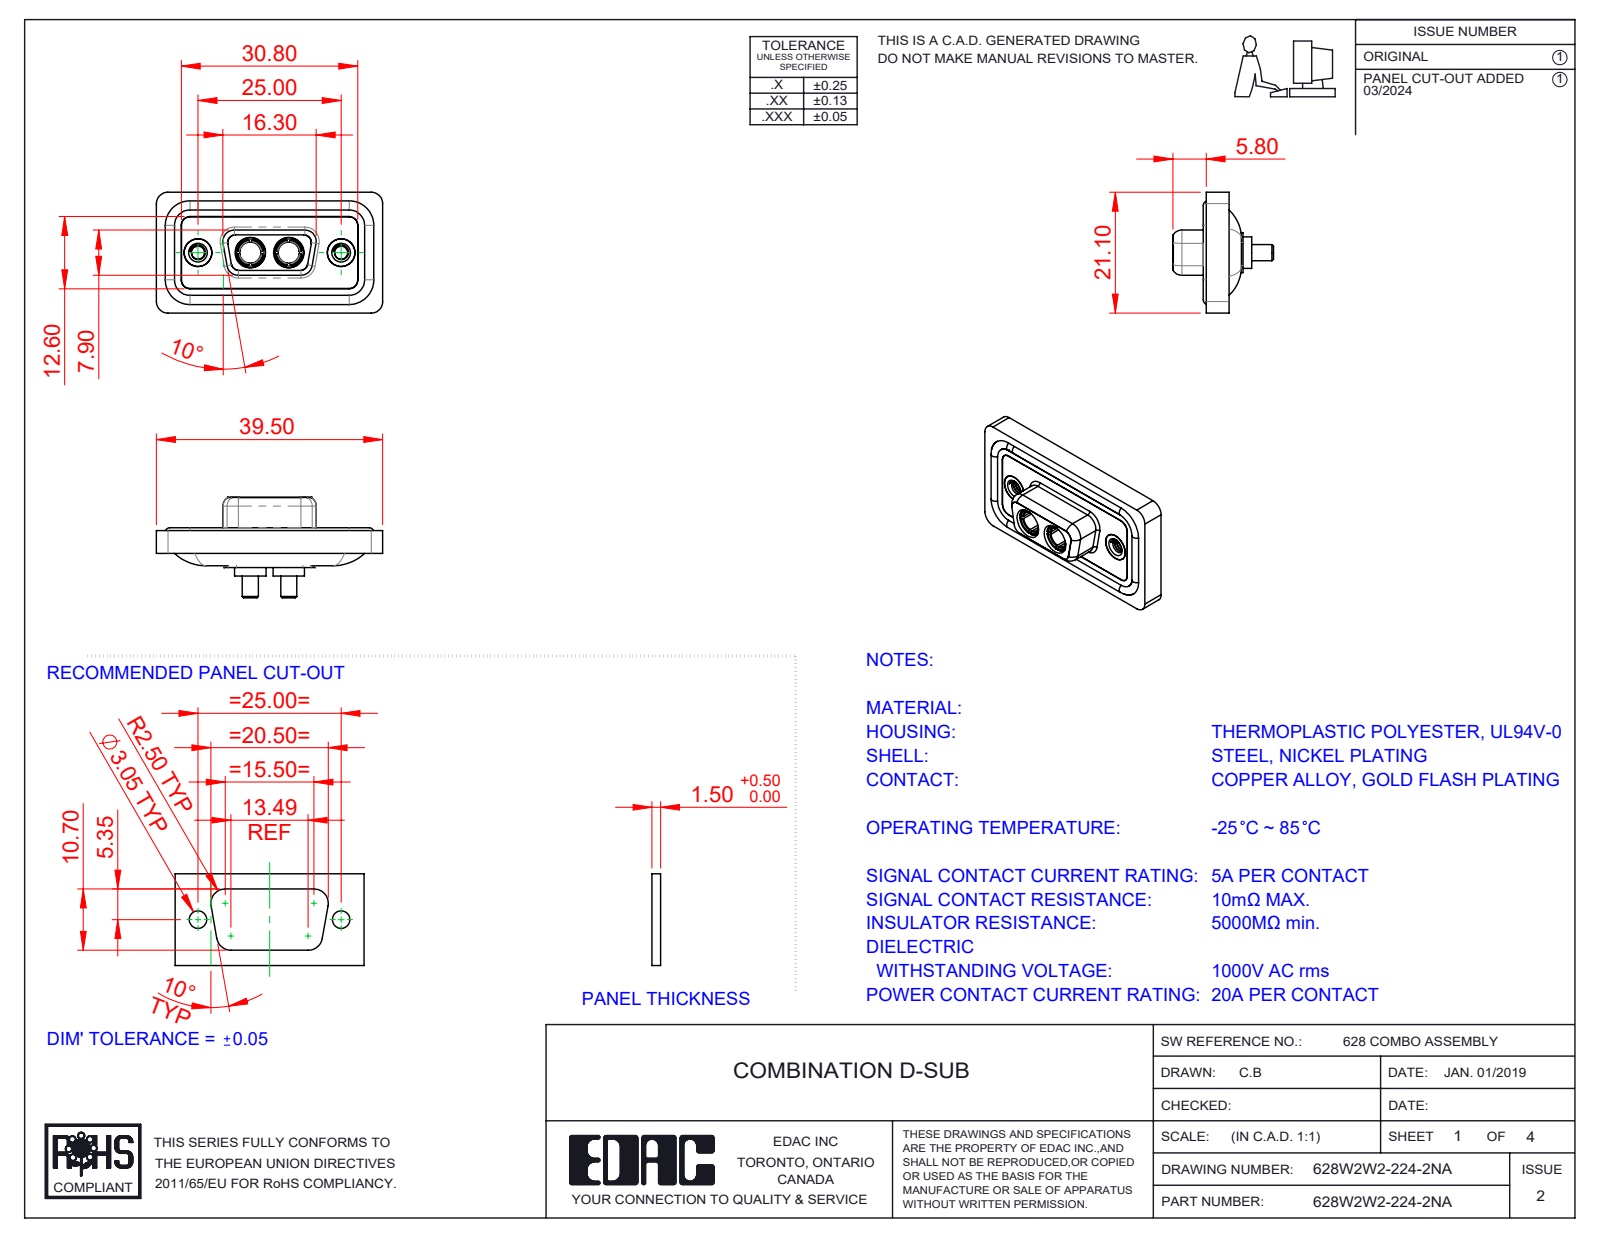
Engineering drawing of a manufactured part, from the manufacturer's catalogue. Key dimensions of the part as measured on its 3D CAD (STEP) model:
Part name (STEP PRODUCT): 628W2W2-224-2NA; 628Combo Threaded Rivet_A; 628Combo Housing_2W2; 628Combo Shell Front_09 Contacts (+3 more)
STEP written by: SolidWorks 2023 (CONFIG_CONTROL_DESIGN)
Units: millimetres
Bodies: 11 solids, 532 faces (163 planar, 236 cylindrical, 133 other)
Overall size (bounding box): 39.5 × 21.1 × 17.55
Volume: 4 714 mm³ · Surface area: 7 633 mm²
Round holes (diameter × count): ⌀4.85 ×4, ⌀2.26 ×2, ⌀3.7 ×2, ⌀4 ×2, ⌀4.05 ×2, ⌀5 ×2, ⌀5.3 ×2
Round bosses / shafts (diameter × count): ⌀1.6 ×4, ⌀5.5 ×2, ⌀5.2 ×2, ⌀4.96 ×2, ⌀4.95 ×2, ⌀4.8 ×2, ⌀4.75 ×2, ⌀3.75 ×2
Partial cylindrical surfaces — rounded edges, fillets, slot ends (radius × count): R1.5 ×22, R2 ×18, R1.35 ×8, R1.6 ×8, R0.25 ×4, R0.5 ×4, R0.6 ×4, R0.65 ×4
Main face-to-face distances: 0.4, 1.8, 1.1, 2.9, 0.5, 1.6, 5.65, 7.45, 1.5, 5.35
Hole centre spacings: 9.14, 15.86, 6.72, 25
